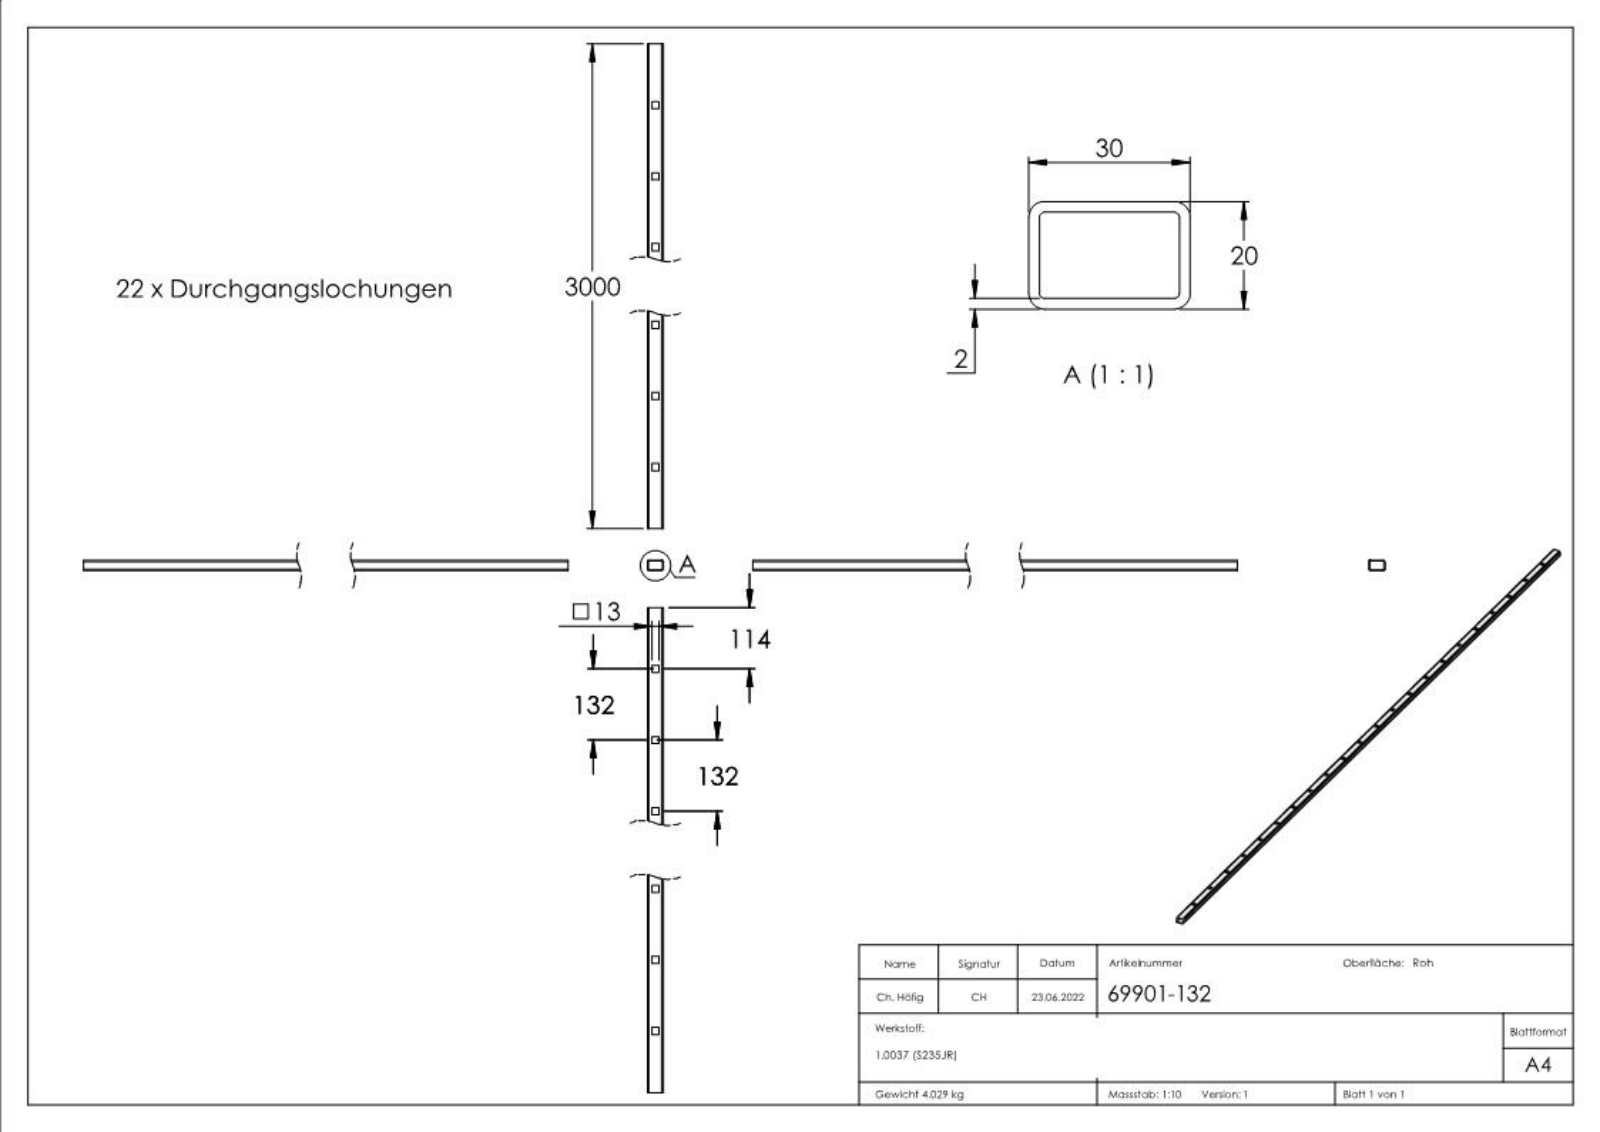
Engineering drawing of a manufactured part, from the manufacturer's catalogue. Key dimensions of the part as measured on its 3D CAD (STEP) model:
Part name (STEP PRODUCT): 69901-132
STEP written by: SolidWorks 2018 (CONFIG_CONTROL_DESIGN)
Units: millimetres
Bodies: 1 solid, 453 faces (321 planar, 8 cylindrical, 124 other)
Overall size (bounding box): 3000 × 30 × 20
Volume: 516 525 mm³ · Surface area: 521 468 mm²
Partial cylindrical surfaces — rounded edges, fillets, slot ends (radius × count): R1 ×4, R3 ×4
Main face-to-face distances: 2, 18, 28, 20, 16, 30, 26, 8.5, 21.5, 6.5
